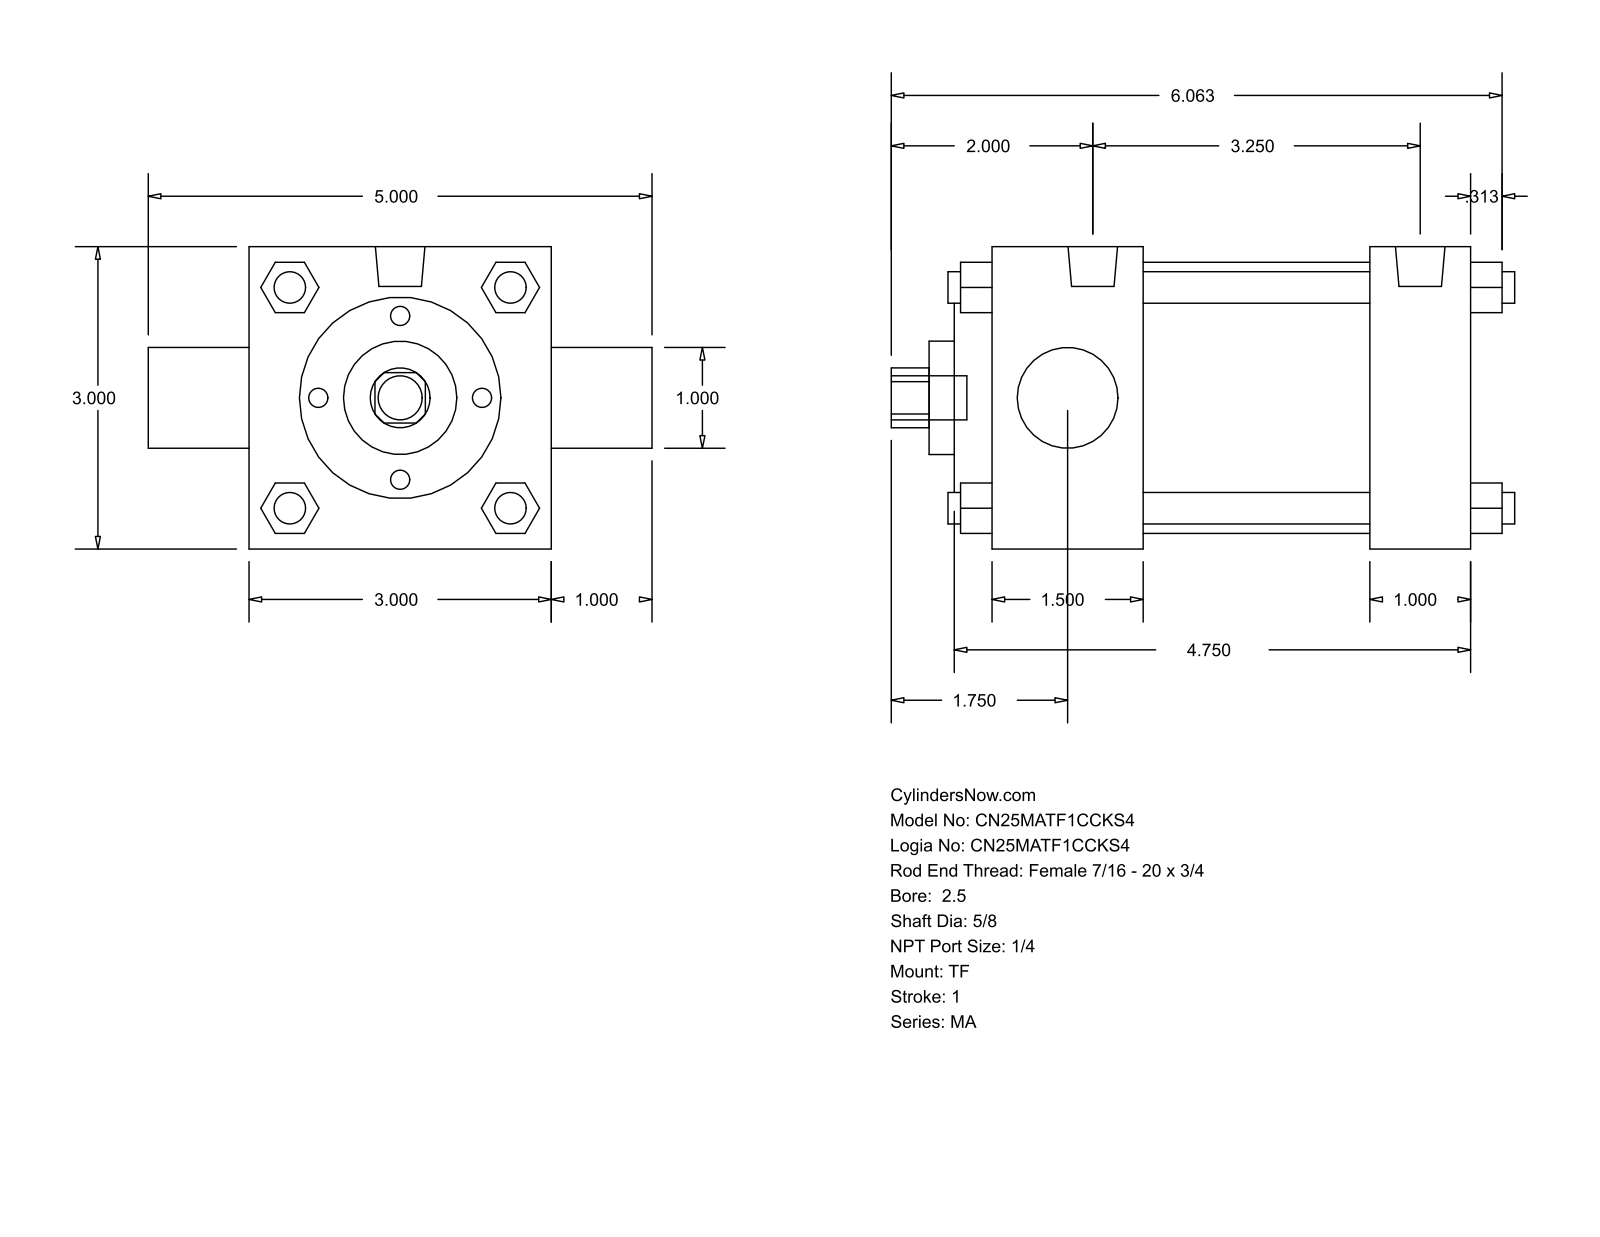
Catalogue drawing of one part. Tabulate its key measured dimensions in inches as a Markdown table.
| quantity | value |
| --- | --- |
| part name | MA_TF__0250_0.625 |
| STEP written by | GSSL Pune (CONFIG_CONTROL_DESIGN) |
| units | inches |
| bodies | 0 solids, 122 faces (93 planar, 29 cylindrical, 0 other) |
| overall size | 6.187 × 5 × 3 |
| round holes (diameter × count) | 0.625 × 1, 1 × 1, 1.125 × 1, 2 × 1, 2.69 × 1 |
| round bosses / shafts (diameter × count) | 0.313 × 7, 0.492 × 2, 0.437 × 1 |
| partial cylindrical surfaces (radius × count) | 0.297 × 1 |
| main face-to-face distances | 3, 4.75, 1, 2.25, 1.5, 3.75, 3.25, 0.5, 0.375, 1.875 |
